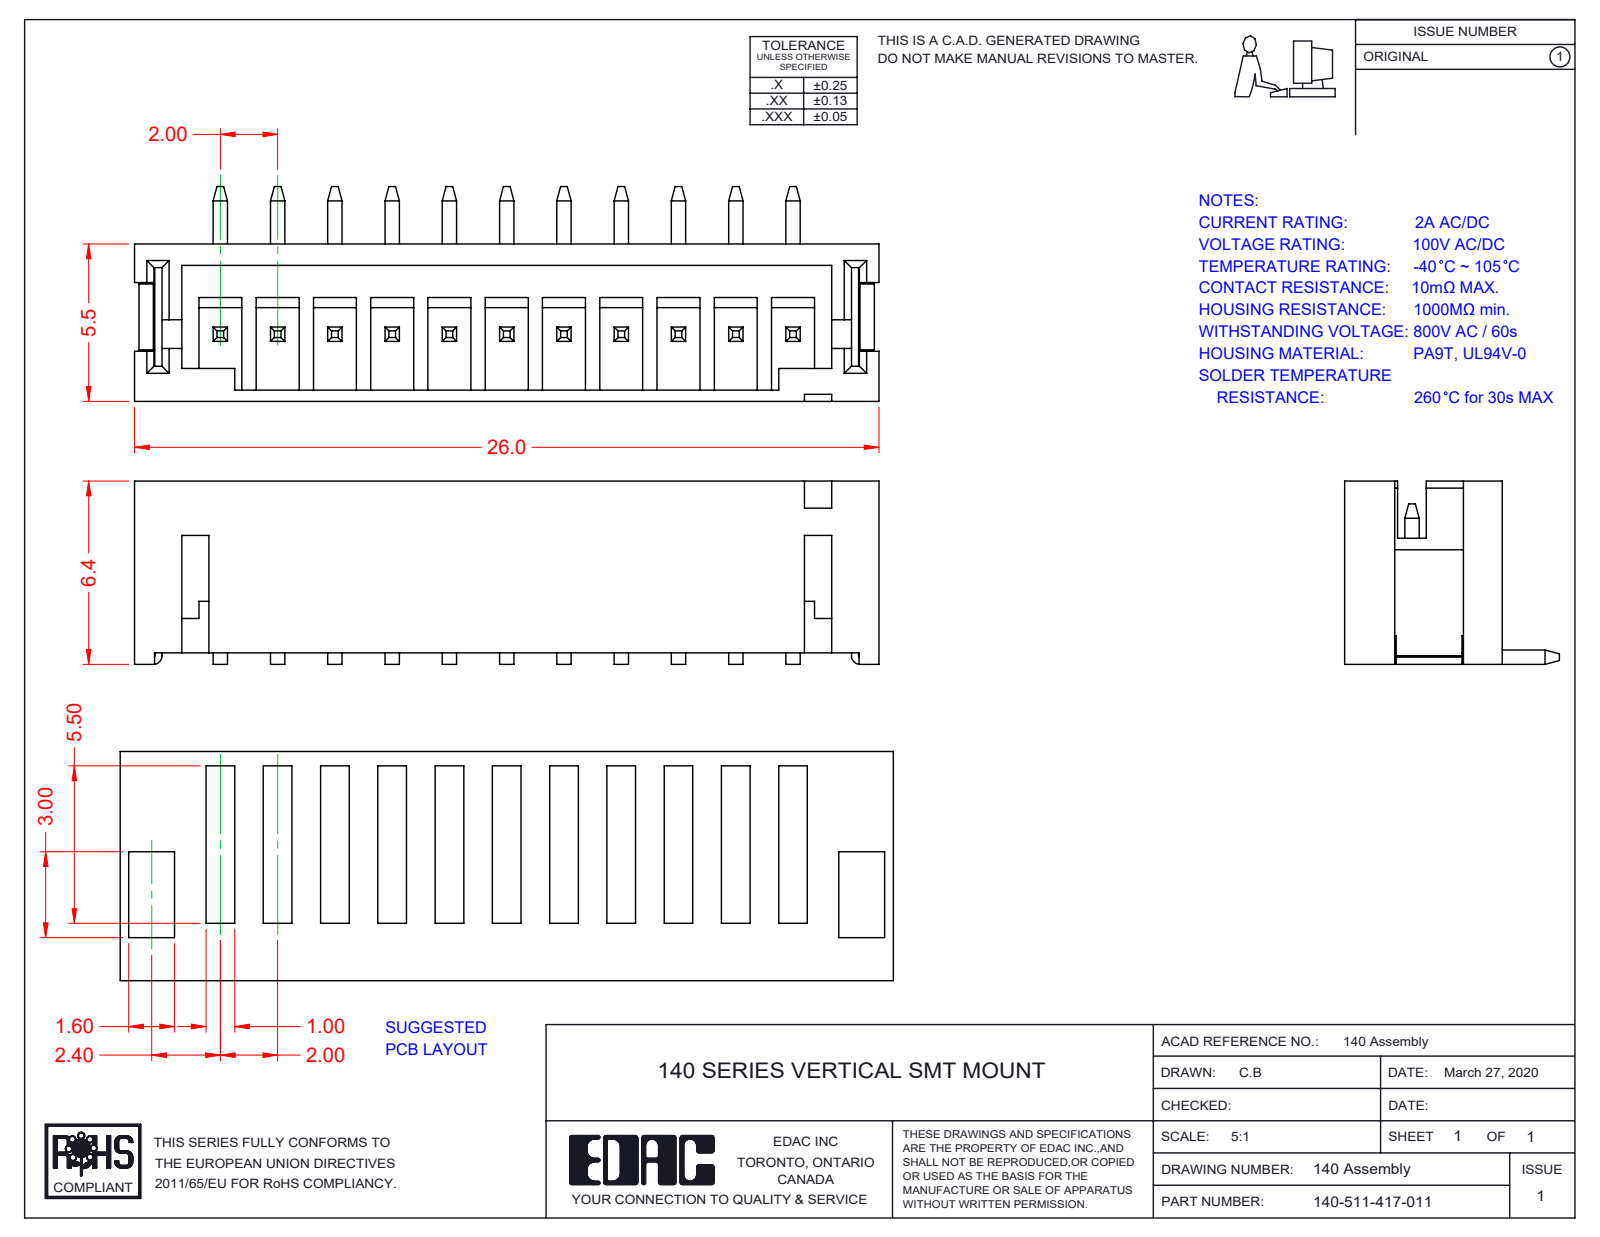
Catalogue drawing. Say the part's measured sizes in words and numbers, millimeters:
The part is named "140-511-417-011; V SMT Pad; V SMT Contact; V SMT Housing_511". Its 3-D file was written by "SolidWorks 2016 (CONFIG_CONTROL_DESIGN)". It is 14 solids with 518 faces: 492 planar, 26 cylindrical and 0 other. Overall it measures 26 by 7.5 by 6.4 millimeters. Its volume is 377 cubic millimeters and its surface area 1 364 square millimeters. Partial cylindrical surfaces (rounded edges, fillets, slot ends): 2 of radius 0.3, 1 of radius 0.55. The main face-to-face distances are 5.5, 0.75, 4.75, 0.4, 0.5, 4.35, 5.1, 0.6, 0.55, 2.2.
